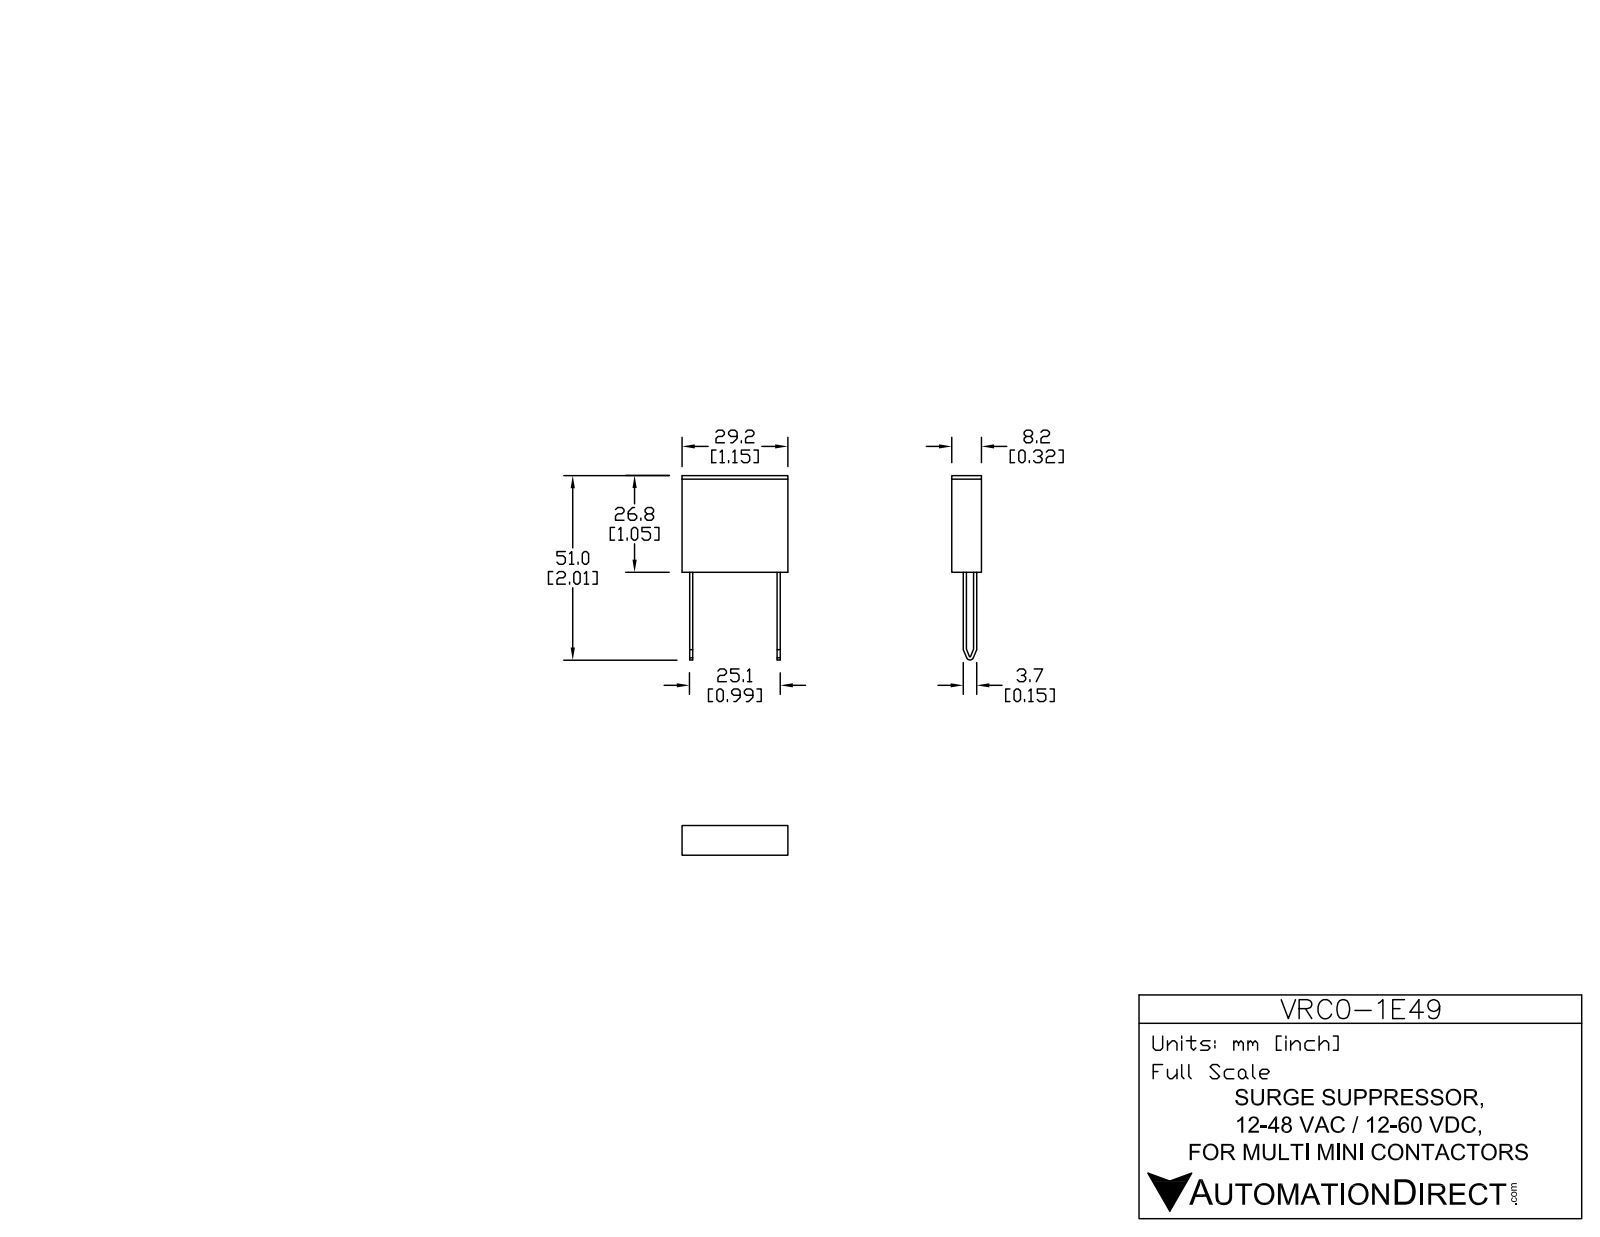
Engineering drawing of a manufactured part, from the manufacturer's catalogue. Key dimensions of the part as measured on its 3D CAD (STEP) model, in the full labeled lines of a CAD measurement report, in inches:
Part name (STEP PRODUCT): VRC0-1E49
STEP written by: SolidWorks 2013 (AUTOMOTIVE_DESIGN)
Units: inches
Bodies: 1 solid, 34 faces (26 planar, 8 cylindrical, 0 other)
Overall size (bounding box): 2.004 × 1.15 × 0.323
Volume: 0.394 in³ · Surface area: 4.345 in²
Partial cylindrical surfaces — rounded edges, fillets, slot ends (radius × count): R0.006 ×1, R0.039 ×1
Main face-to-face distances: 0.323, 1.051, 1.15, 0.033, 0.083, 1.067, 0.116, 1.033, 0.951, 0.112
